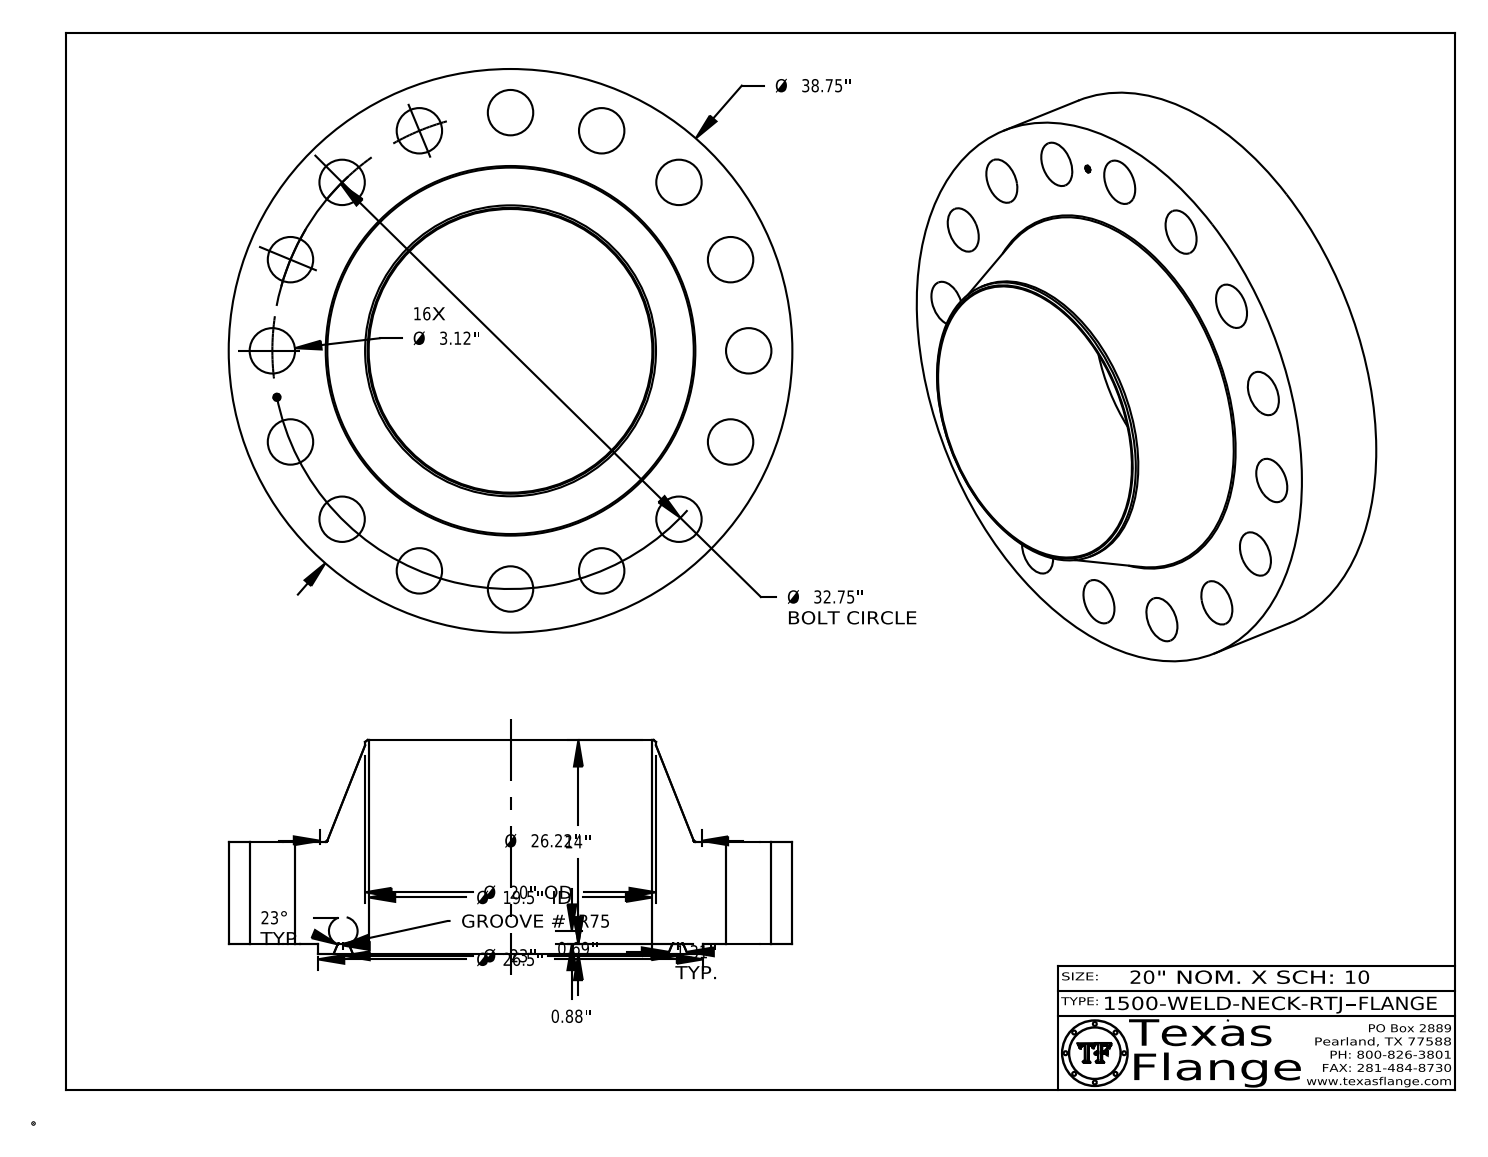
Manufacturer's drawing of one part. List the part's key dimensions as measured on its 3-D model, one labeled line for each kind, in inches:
Part name (STEP PRODUCT): 1500-WELD-NECK-RTJ
STEP written by: CATIA V5 STEP AP214 (AUTOMOTIVE_DESIGN)
Units: inches
Bodies: 1 solid, 445 faces (371 planar, 60 cylindrical, 14 other)
Overall size (bounding box): 38.75 × 38.75 × 14.688
Volume: 6 135 in³ · Surface area: 4 824 in²
Round holes (diameter × count): ⌀3.12 ×16, ⌀0.495 ×1, ⌀19.5 ×1
Round bosses / shafts (diameter × count): ⌀0.03 ×8, ⌀38.75 ×1, ⌀26.5 ×1, ⌀20 ×1, ⌀0.39 ×1
Main face-to-face distances: 7, 0.688, 7.688, 14.688, 14, 7.673, 6.985, 0.015, 7.015, 0.148
Hole centre spacings: 18.195, 16.375, 12.533, 23.157, 30.257, 6.389, 6.389, 27.23
